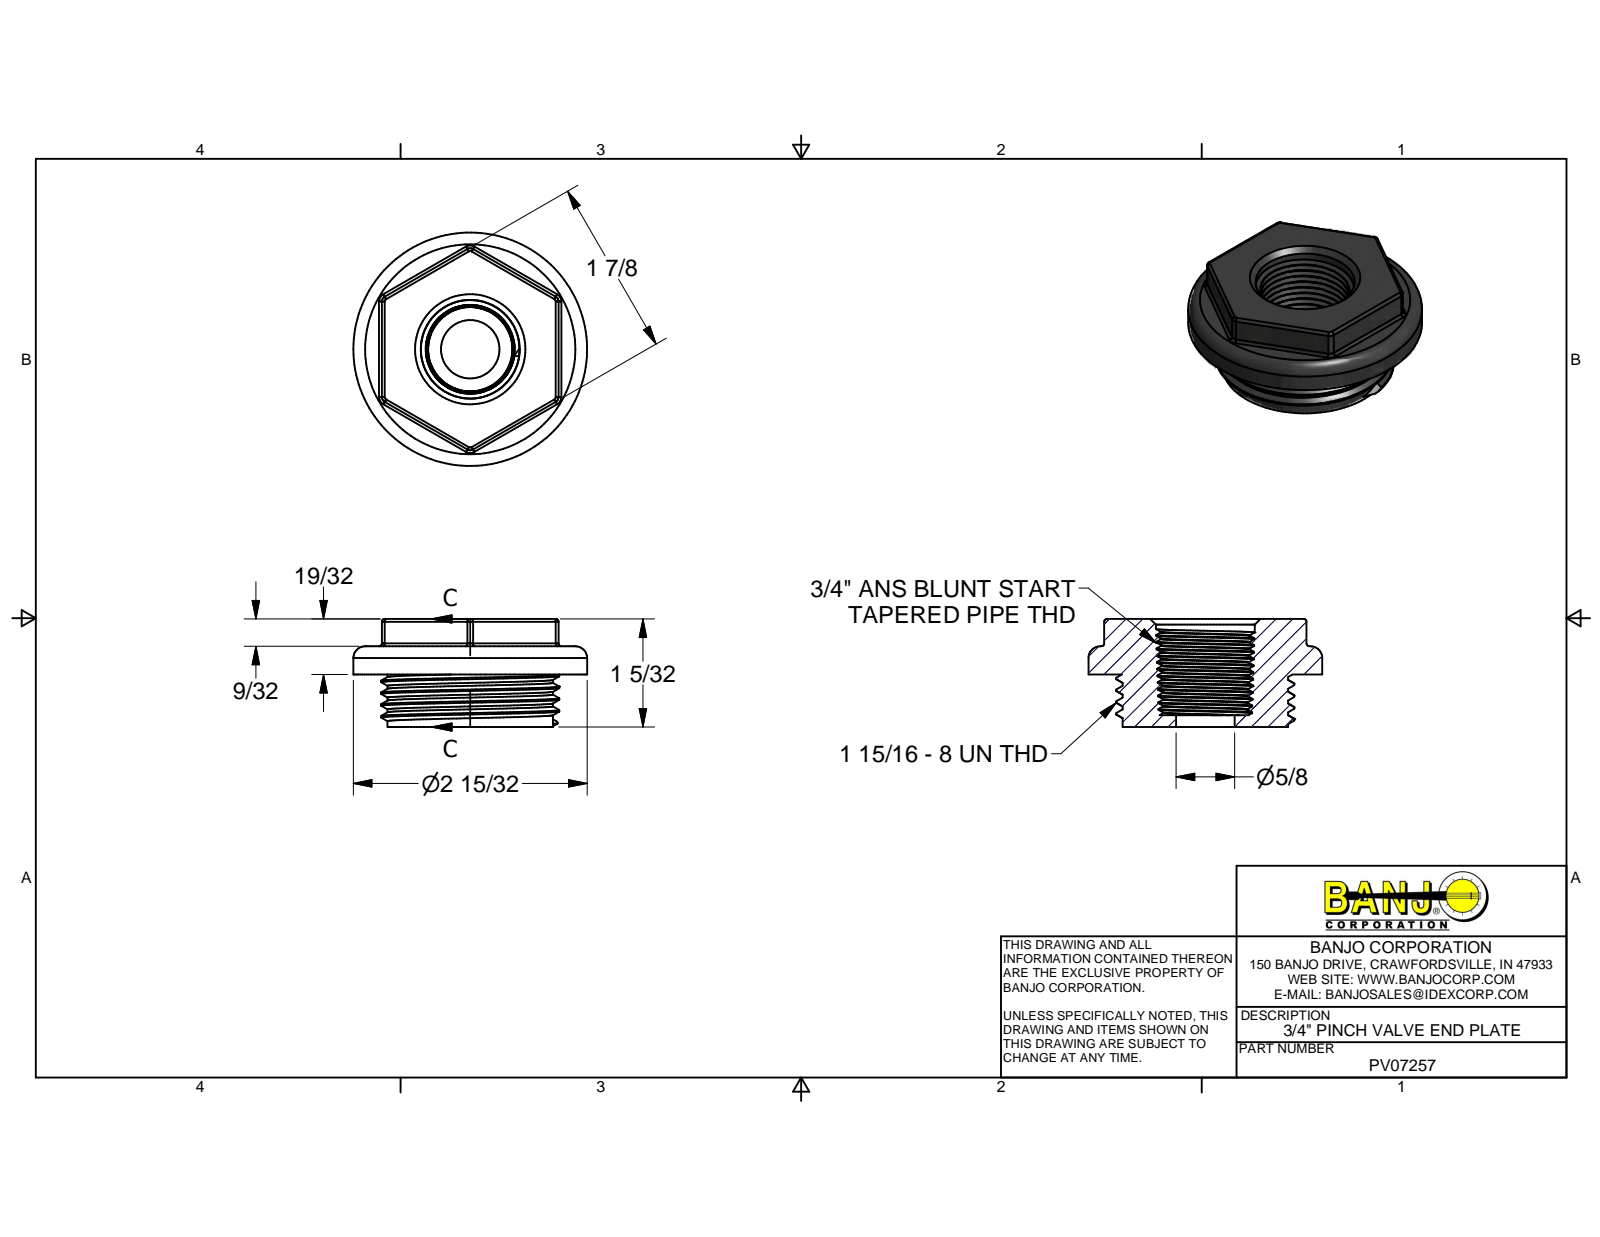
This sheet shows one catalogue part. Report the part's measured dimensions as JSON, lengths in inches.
{"part_name": "PV07257", "step_written_by": "Autodesk Inventor 2013 (AUTOMOTIVE_DESIGN)", "units": "inches", "bodies": {"solids": 1, "faces": 76, "planar": 13, "cylindrical": 26, "other": 37}, "overall_size": [2.48, 2.48, 1.148], "volume_in3": 2.925, "surface_area_in2": 22.82, "round_holes": [[0.62, 1]], "round_bosses_or_shafts": [[2.48, 1], [1.89, 1], [1.755, 1]], "partial_cylinders_radius": [[0.03, 12], [0.06, 6]], "face_to_face_distances": [0.558, 0.59, 1.148, 1.875, 0.29, 0.3, 0.858, 1.023, 0.733, 0.433]}
